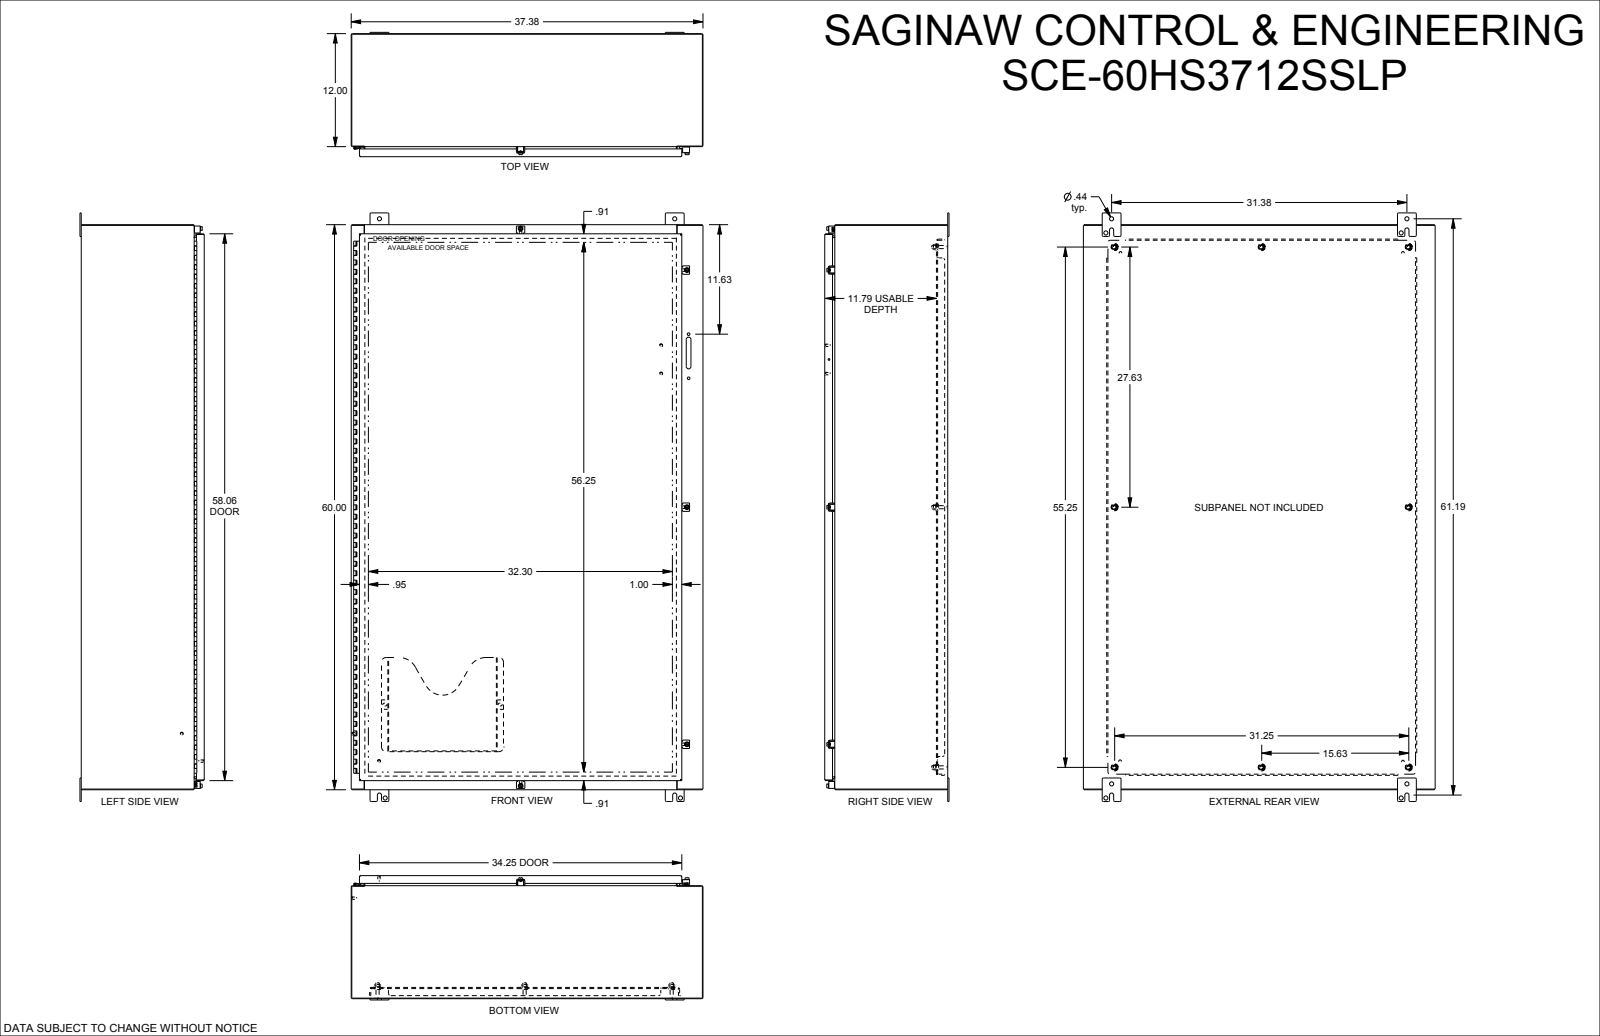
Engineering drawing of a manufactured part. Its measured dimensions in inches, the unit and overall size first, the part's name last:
Units: inches
Overall size (bounding box): 62.5 × 37.375 × 13.343
Round holes (diameter × count): ⌀0.367 ×8, ⌀0.5 ×8, ⌀0.172 ×6, ⌀0.205 ×6, ⌀0.244 ×6, ⌀0.281 ×6, ⌀0.312 ×6, ⌀0.375 ×6, ⌀0.203 ×5, ⌀0.31 ×4, ⌀0.04 ×3, ⌀0.218 ×3
Round bosses / shafts (diameter × count): ⌀0.25 ×11, ⌀0.248 ×11, ⌀0.17 ×9, ⌀0.366 ×8, ⌀0.332 ×8, ⌀0.24 ×6, ⌀0.507 ×5, ⌀0.59 ×4
Partial cylindrical surfaces — rounded edges, fillets, slot ends (radius × count): R0.01 ×214, R0.025 ×76, R0.015 ×28, R0.185 ×21, R0.04 ×20, R0.06 ×16, R0.06 ×16, R0.1 ×16
Main face-to-face distances: 0.075, 12.993, 12.918, 13.068, 1.125, 1.2, 11.868, 11.793, 0.125, 1.075
Hole centre spacings: 25.25, 58.5, 0.494, 25.742, 28.825, 29.319, 29.807, 33.141
Volume: 840.5 in³ · Surface area: 19 195 in²
Bodies: 83 solids, 3710 faces (1424 planar, 1110 cylindrical, 1176 other)
Part name (STEP PRODUCT): SCE-60HS3712LP
STEP written by: SolidWorks 2021 (AUTOMOTIVE_DESIGN)
